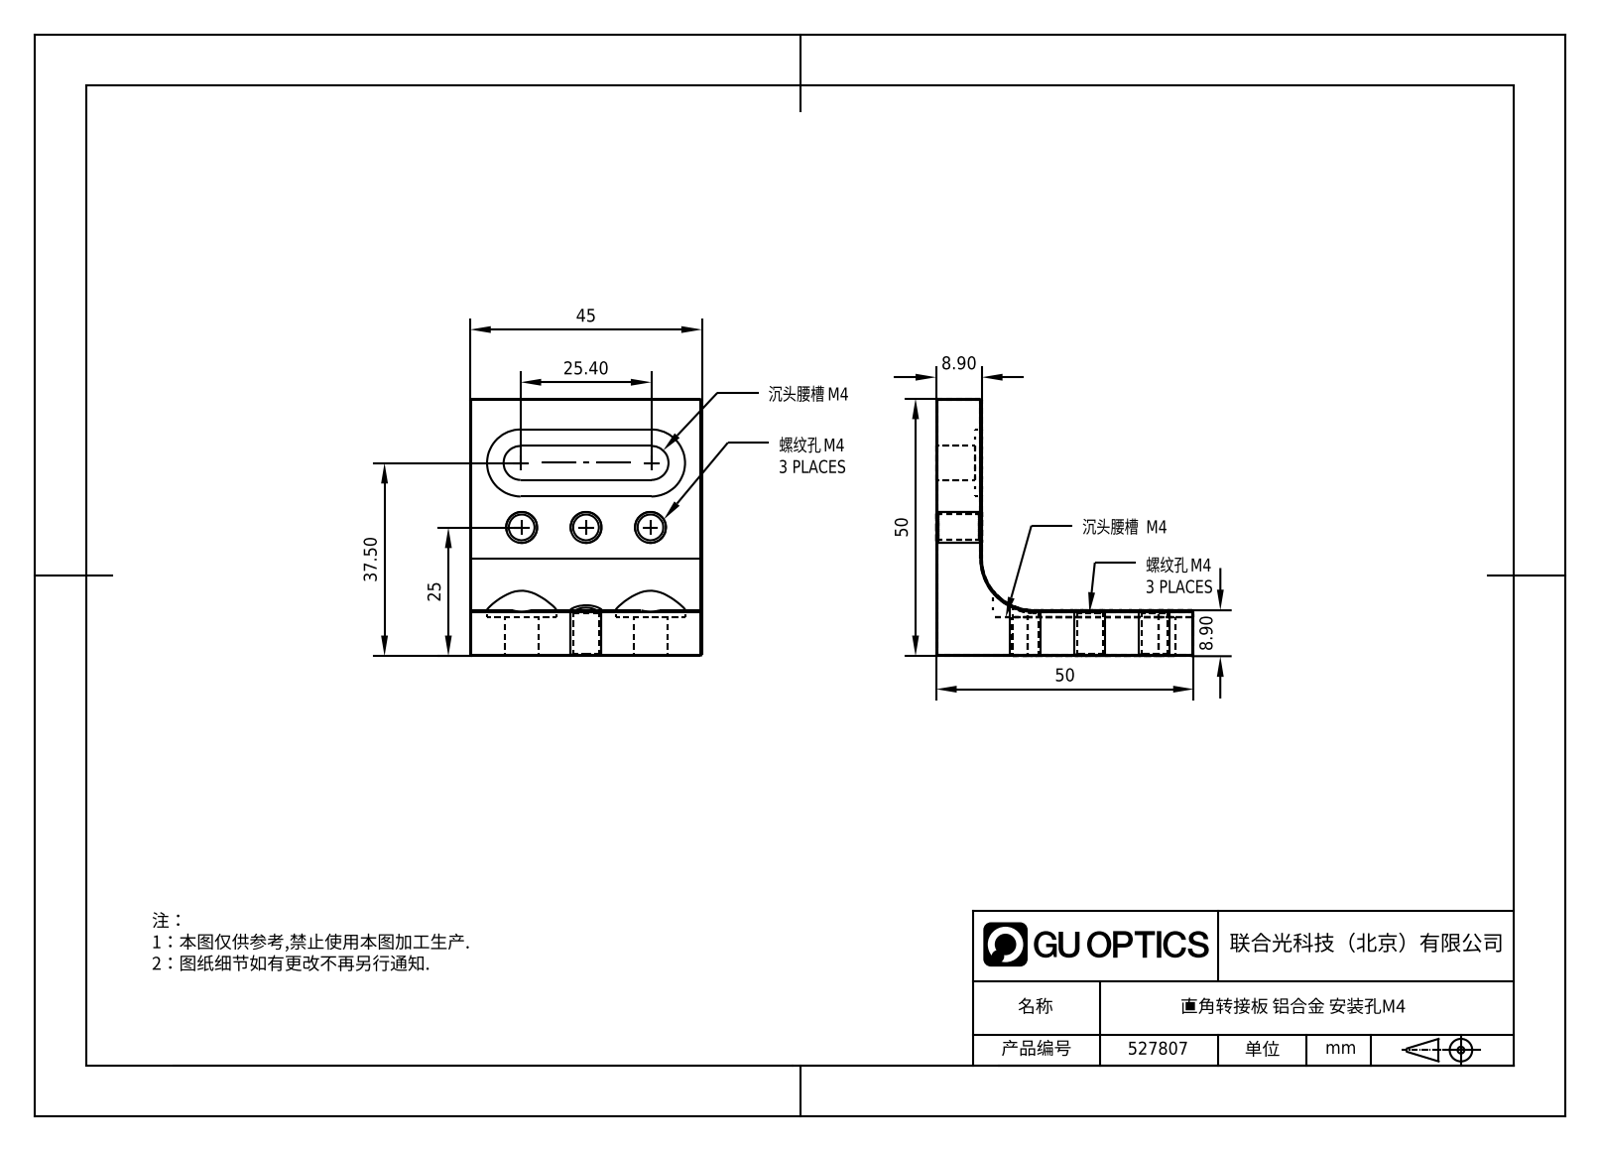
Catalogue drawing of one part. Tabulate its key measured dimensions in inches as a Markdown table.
| quantity | value |
| --- | --- |
| part name | 7.5.4.10_MCS-50C1 |
| STEP written by | SolidWorks 2021 (CONFIG_CONTROL_DESIGN) |
| units | inches |
| bodies | 1 solid, 106 faces (50 planar, 31 cylindrical, 25 other) |
| overall size | 1.969 × 1.969 × 1.772 |
| volume | 1.971 in³ |
| surface area | 18.38 in² |
| round holes (diameter × count) | 0.13 × 6 |
| partial cylindrical surfaces (radius × count) | 0.091 × 6, 0.207 × 6, 0.394 × 1 |
| main face-to-face distances | 0.35, 1.772, 1.969, 1.618, 0.295, 0.055, 1.673, 0.181, 0.984, 0.303 |
| hole center spacings | 0.492, 0.984 |
